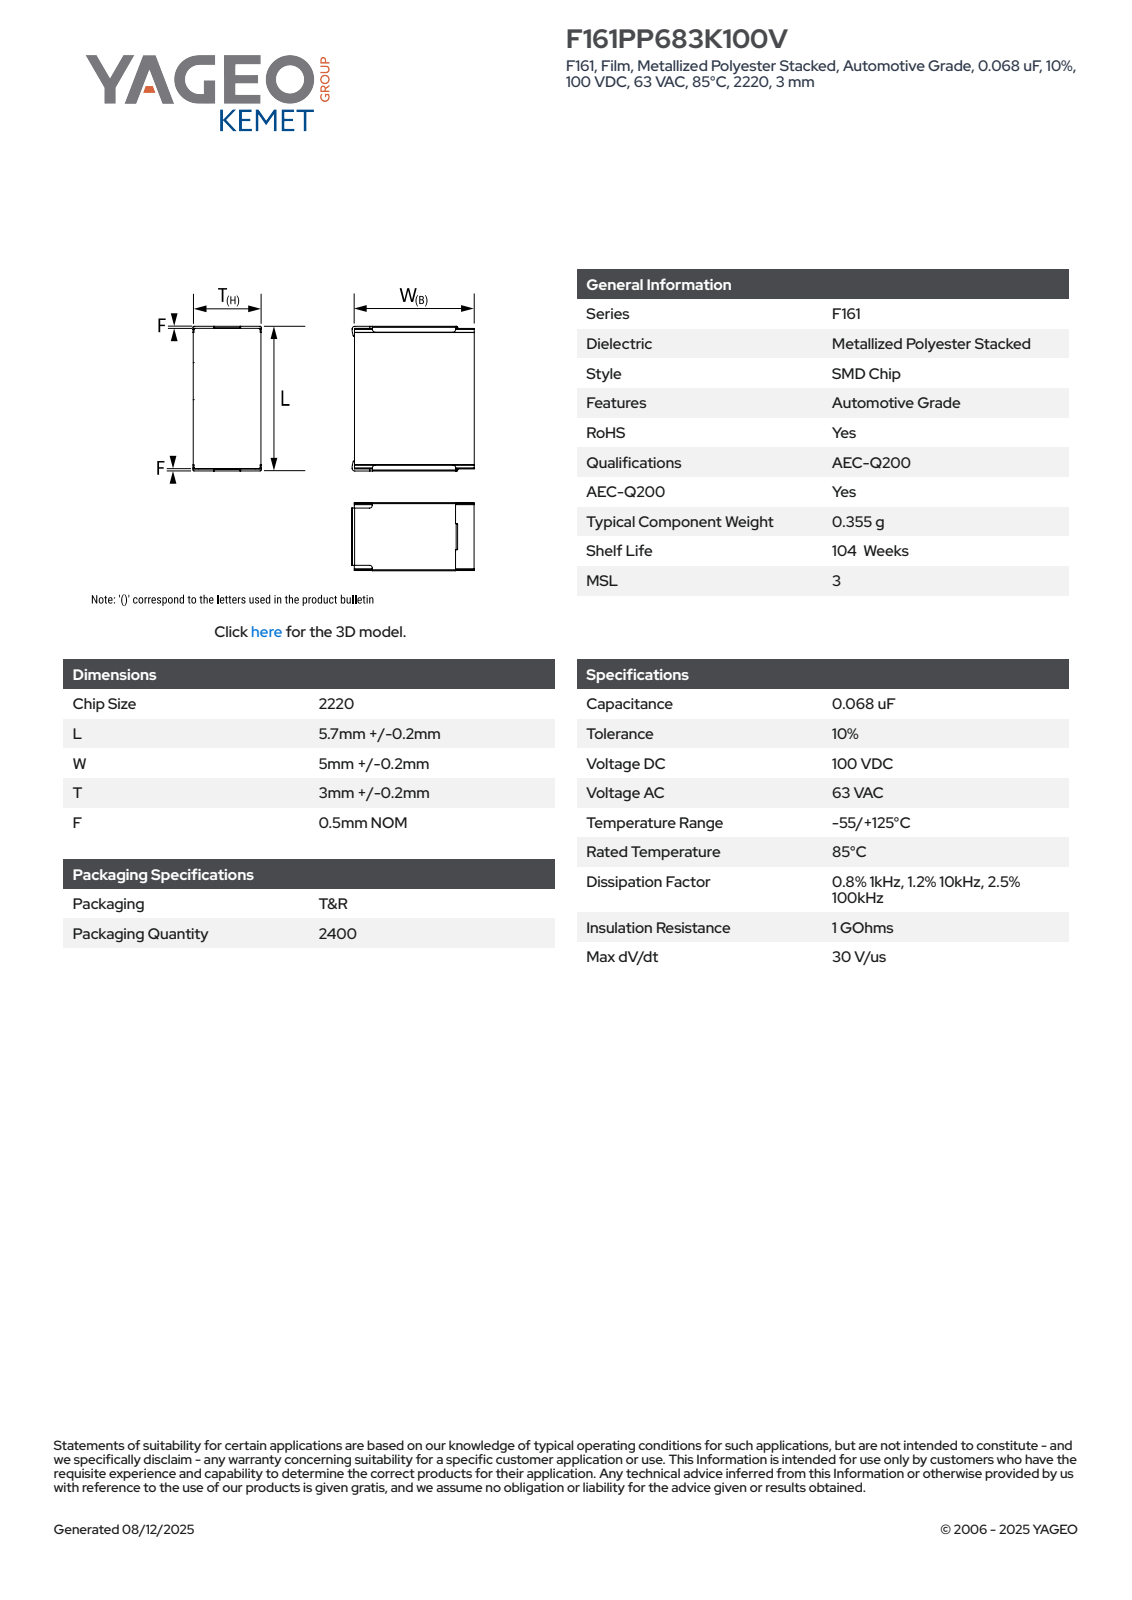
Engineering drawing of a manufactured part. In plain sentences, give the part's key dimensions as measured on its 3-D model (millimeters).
The part is named "CFS_KSTD_2220_L5.9W5.2T3.2F0.5". Its 3-D file was written by "SolidWorks 2021 (AUTOMOTIVE_DESIGN)". It is 4 solids with 117 faces: 103 planar, 14 cylindrical and 0 other. Overall it measures 5.9 by 5.37 by 3.36 millimeters. Its volume is 92 cubic millimeters and its surface area 138 square millimeters. Partial cylindrical surfaces (rounded edges, fillets, slot ends): 10 of radius 0.19, 4 of radius 0.21. The main face-to-face distances are 3.2, 4.99, 5.9, 0.5, 5.4, 3.28, 4.9, 0.38, 3.36, 5.37.
